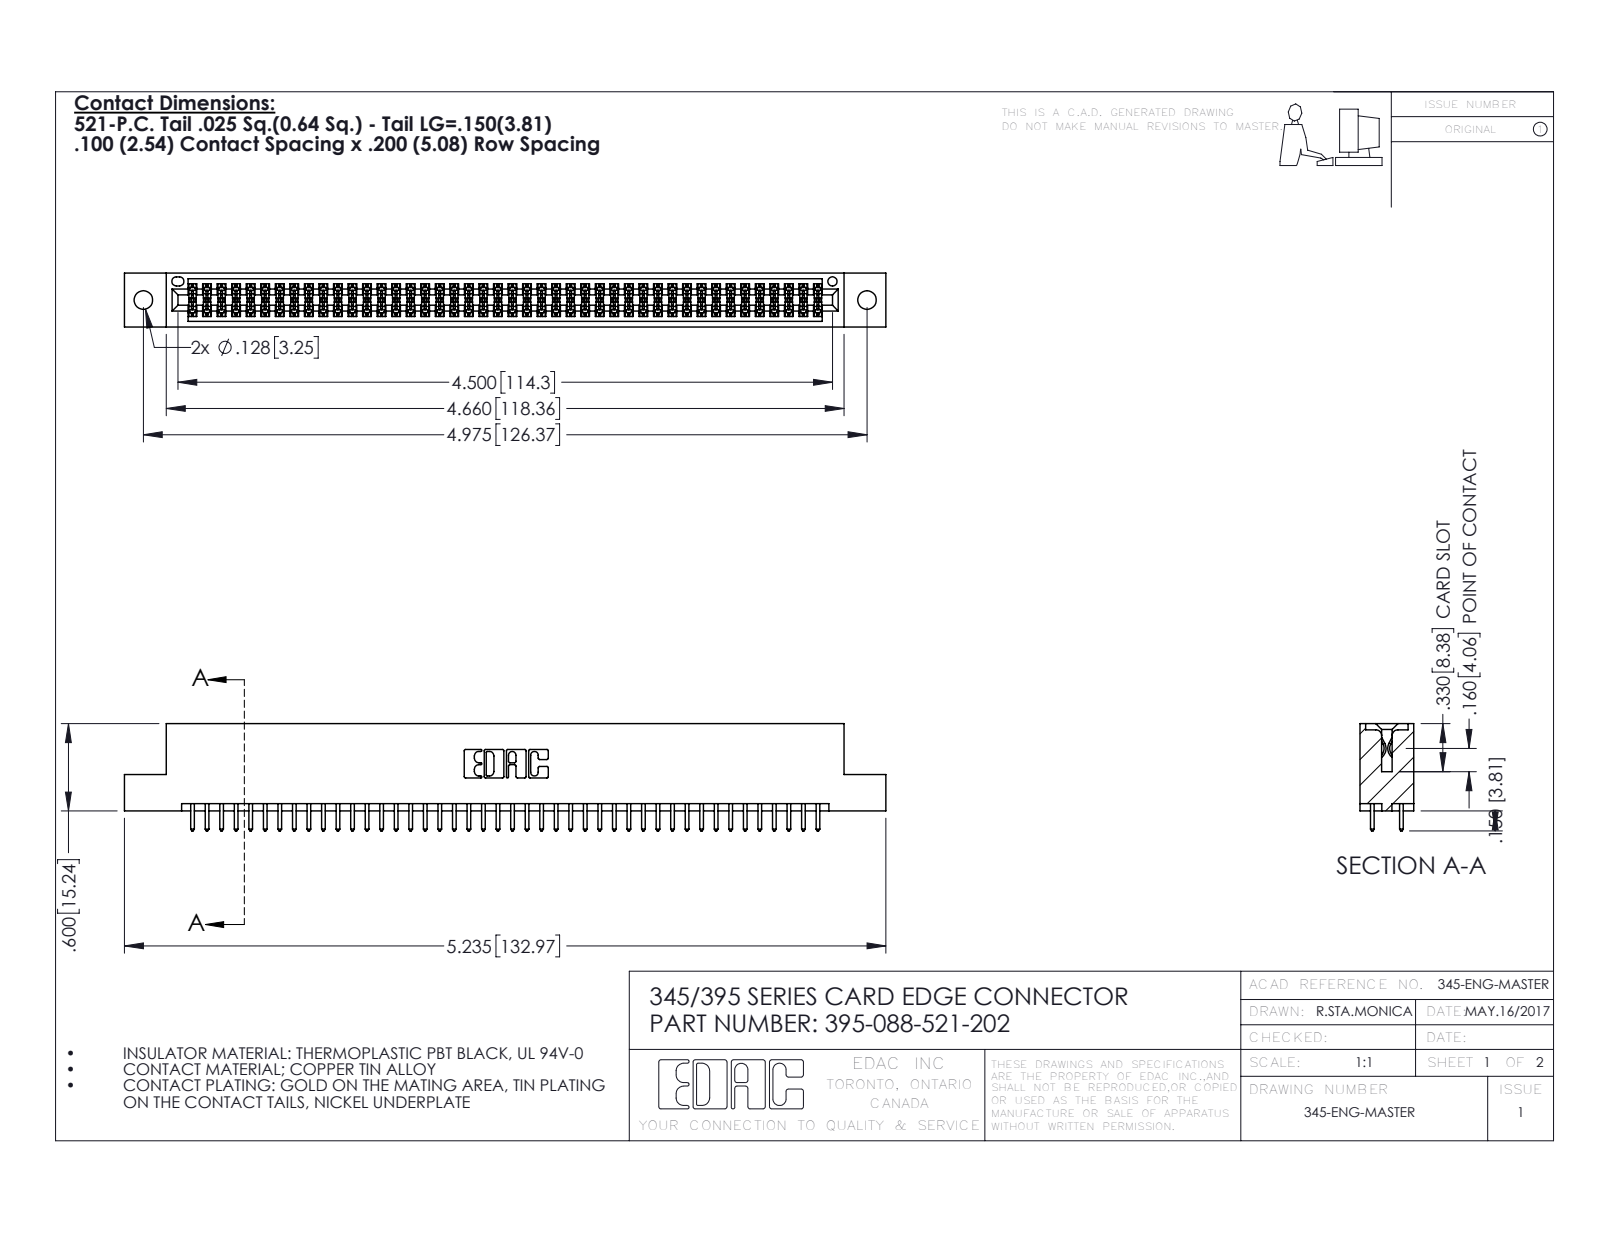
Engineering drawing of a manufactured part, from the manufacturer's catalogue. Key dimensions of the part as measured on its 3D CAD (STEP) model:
Part name (STEP PRODUCT): 345-292-001_345-293-121; 345 Part_Flush Mounting Lugs - 0.128 Dia; 395-088-521-202
STEP written by: SolidWorks 2016 (CONFIG_CONTROL_DESIGN)
Units: inches
Bodies: 89 solids, 4526 faces (2984 planar, 1542 cylindrical, 0 other)
Overall size (bounding box): 5.235 × 0.737 × 0.37
Volume: 0.785 in³ · Surface area: 28.75 in²
Round holes (diameter × count): ⌀0.128 ×2, ⌀0.064 ×1
Partial cylindrical surfaces — rounded edges, fillets, slot ends (radius × count): R0.006 ×132, R0.01 ×88, R0.01 ×22, R0.007 ×6, R0.031 ×6, R0.026 ×3, R0.014 ×2, R0.019 ×2
Main face-to-face distances: 0.298, 0.072, 0.2, 0.37, 0.098, 0.272, 0.025, 0.225, 0.175, 0.149
Hole centre spacings: 0.27, 4.739, 4.975
